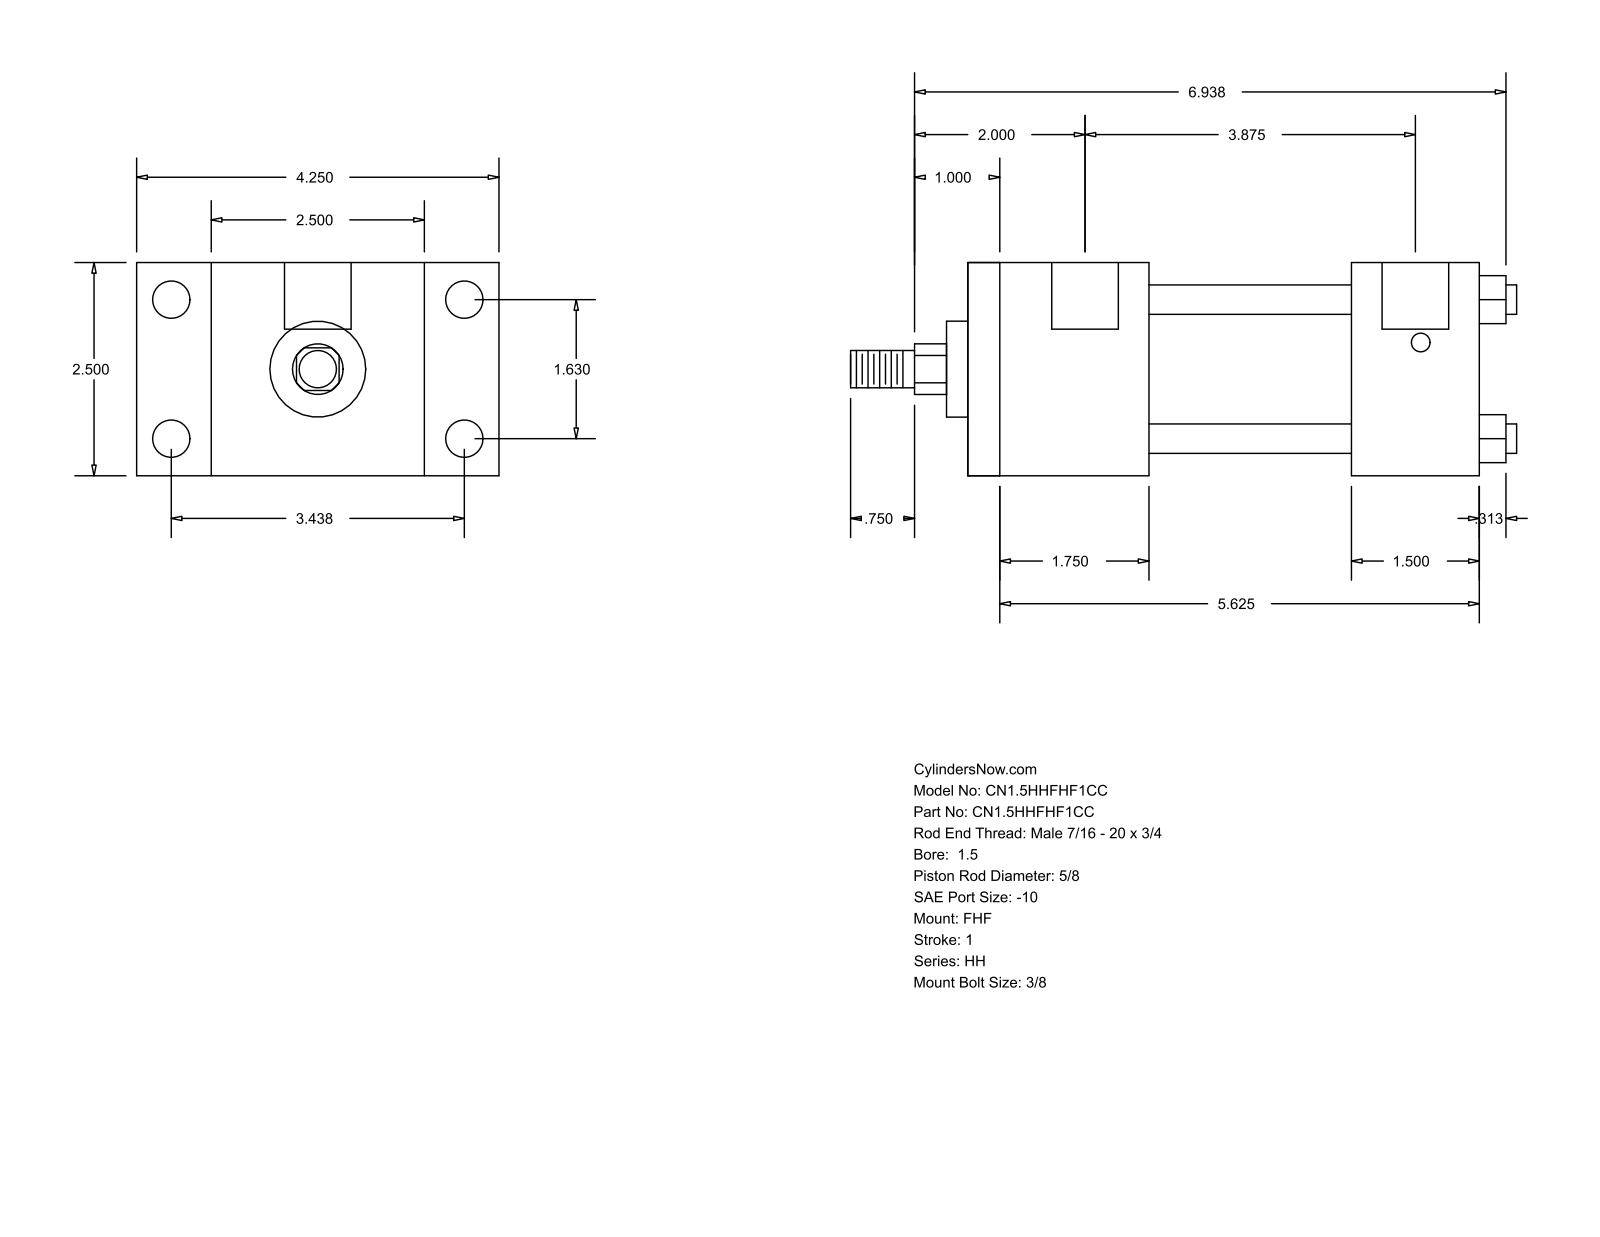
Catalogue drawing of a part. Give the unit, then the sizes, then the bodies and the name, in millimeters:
Units: millimetres
Overall size (bounding box): 198.44 × 107.95 × 63.5
Round holes (diameter × count): ⌀5.56 ×4, ⌀11.13 ×4, ⌀19.84 ×2
Round bosses / shafts (diameter × count): ⌀8.76 ×4, ⌀44.45 ×1, ⌀28.57 ×1, ⌀15.88 ×1, ⌀11.11 ×1
Partial cylindrical surfaces — rounded edges, fillets, slot ends (radius × count): R7.54 ×1
Main face-to-face distances: 63.5, 22.23, 85.73, 53.97, 107.96, 152.4, 98.43, 38.1, 60.33, 114.3
Hole centre spacings: 1.59, 41.4, 87.32, 96.64, 100.01, 101.6, 98.42
Bodies: 0 solids, 88 faces (60 planar, 28 cylindrical, 0 other)
Part name (STEP PRODUCT): HH_FHF__0150_0.625
STEP written by: GSSL Pune (CONFIG_CONTROL_DESIGN)
